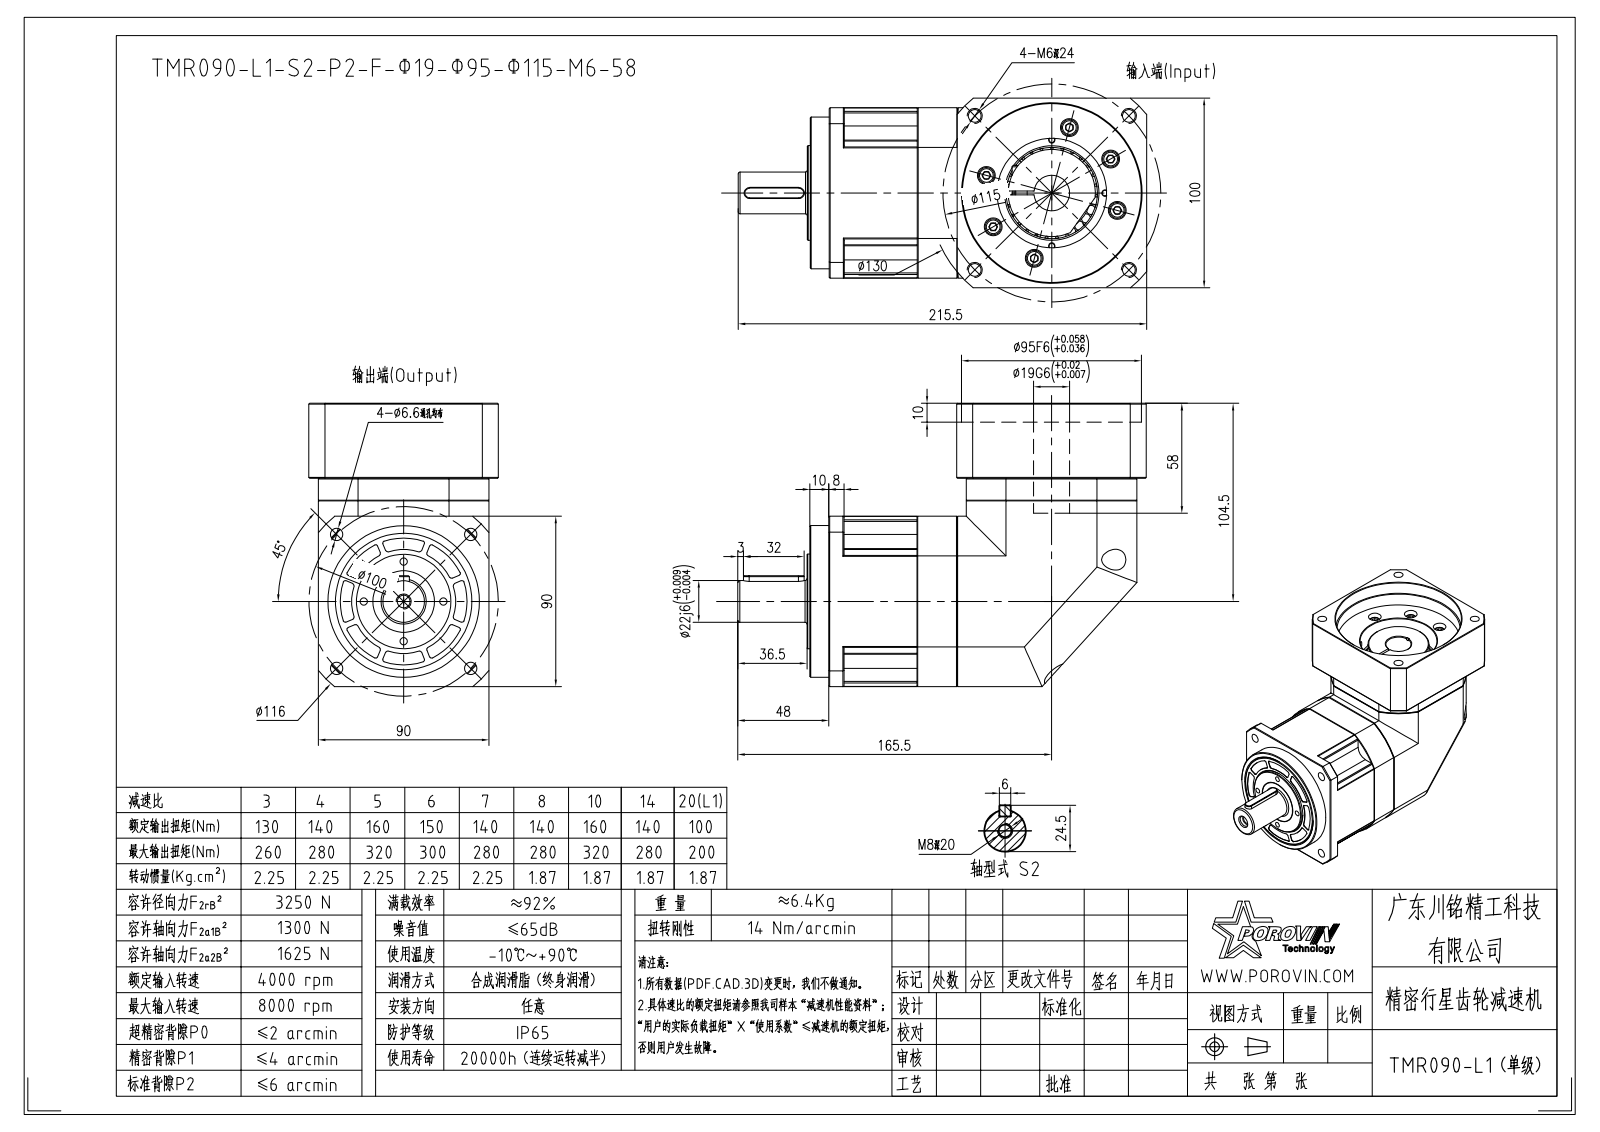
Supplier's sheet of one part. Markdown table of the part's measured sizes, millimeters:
| quantity | value |
| --- | --- |
| part name | HEXAGON_SOCKET_HEAD_CAP_S-15030; HEXAGON_SOCKET_HEAD_CAP_SC-4404; TMR900004; SPRING_LOCK_WASHERS--NORM-14923 (+8 more) |
| STEP written by | CREO PARAMETRIC BY PTC INC, 2020053 (CONFIG_CONTROL_DESIGN) |
| units | millimeters |
| bodies | 42 solids, 1276 faces (513 planar, 542 cylindrical, 221 other) |
| overall size | 215.5 × 149.5 × 100 |
| volume | 1 405 000 mm³ |
| surface area | 224 112 mm² |
| round holes (diameter × count) | 5.4 × 12, 5.5 × 12, 9.5 × 12, 4.2 × 7, 5 × 5, 6.5 × 5, 4 × 4, 6.6 × 4, 6.68 × 4, 11 × 4, 6.8 × 1, 8.4 × 1 |
| round bosses / shafts (diameter × count) | 8.5 × 12, 8 × 12, 5 × 12, 10 × 4, 9.88 × 4, 6 × 4, 80 × 1, 78 × 1 |
| partial cylindrical surfaces (radius × count) | 1 × 92, 7.5 × 4, 51 × 3, 3 × 2, 4 × 1, 5.25 × 1, 40 × 1, 50.25 × 1 |
| main face-to-face distances | 5, 90, 12, 95, 21.3, 21.5, 31.5, 20, 51.5, 10 |
| hole center spacings | 35.75, 27.36, 38.16, 66.06, 66.53, 75.16, 24.76, 59.34 |
